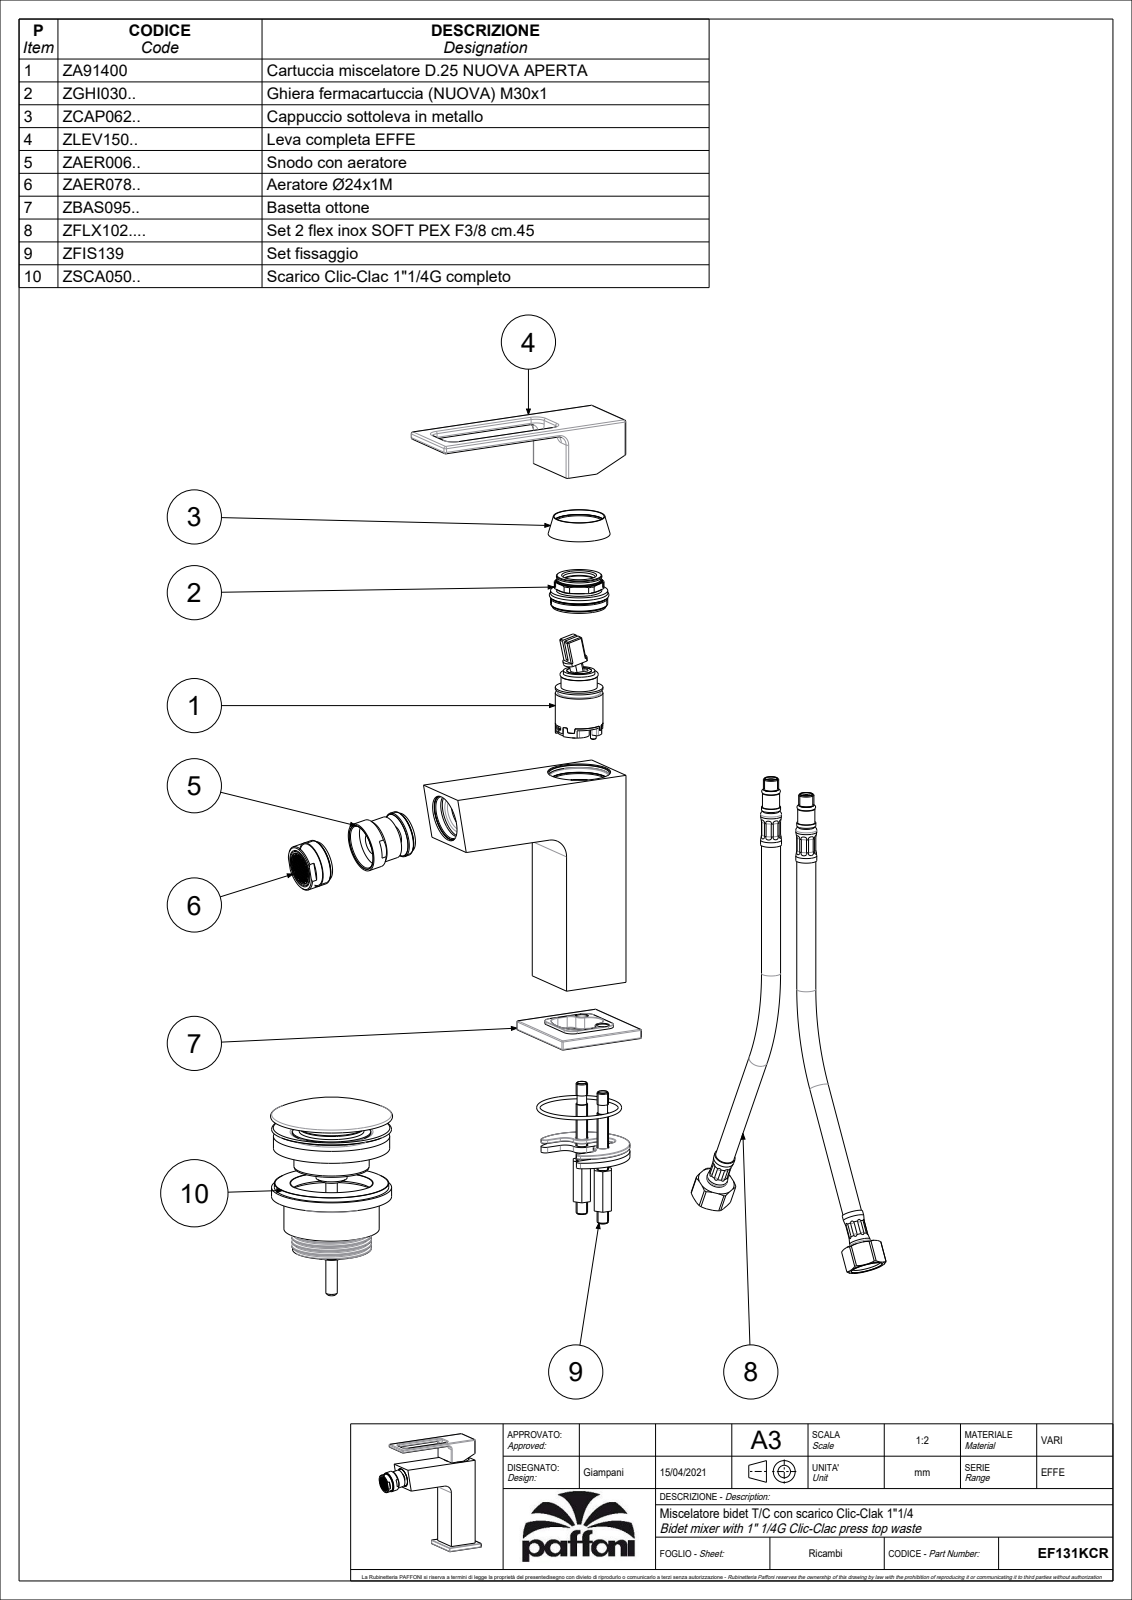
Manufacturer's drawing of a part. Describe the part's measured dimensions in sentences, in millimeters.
The part is named "EF131CR". Its 3-D file was written by "CREO PARAMETRIC BY PTC INC, 2020044 (CONFIG_CONTROL_DESIGN)". It is 4 solids with 1935 faces: 1552 planar, 216 cylindrical and 167 other. Overall it measures 145.58 by 136.42 by 48 millimeters. Its volume is 117 293 cubic millimeters and its surface area 73 763 square millimeters. Round holes: 3 of diameter 5.5, 2 of diameter 6.2, 2 of diameter 23, 1 of diameter 3, 1 of diameter 4.2, 1 of diameter 4.5, 1 of diameter 7.8, 1 of diameter 8, 1 of diameter 15.5, 1 of diameter 16, 1 of diameter 17, 1 of diameter 20. Round bosses or shafts: 1 of diameter 41.8, 1 of diameter 25.8, 1 of diameter 24, 1 of diameter 22.5, 1 of diameter 21, 1 of diameter 19.5, 1 of diameter 18.8, 1 of diameter 16.8. Partial cylindrical surfaces (rounded edges, fillets, slot ends): 62 of radius 1, 14 of radius 0.5, 11 of radius 5, 8 of radius 1.5, 6 of radius 0.25, 6 of radius 4, 2 of radius 3.5, 2 of radius 7. The main face-to-face distances are 3, 33, 36, 30, 26, 28.08, 29, 57.08, 9, 4. The hole center spacings are 11.4, 13.6, 11, 22.
